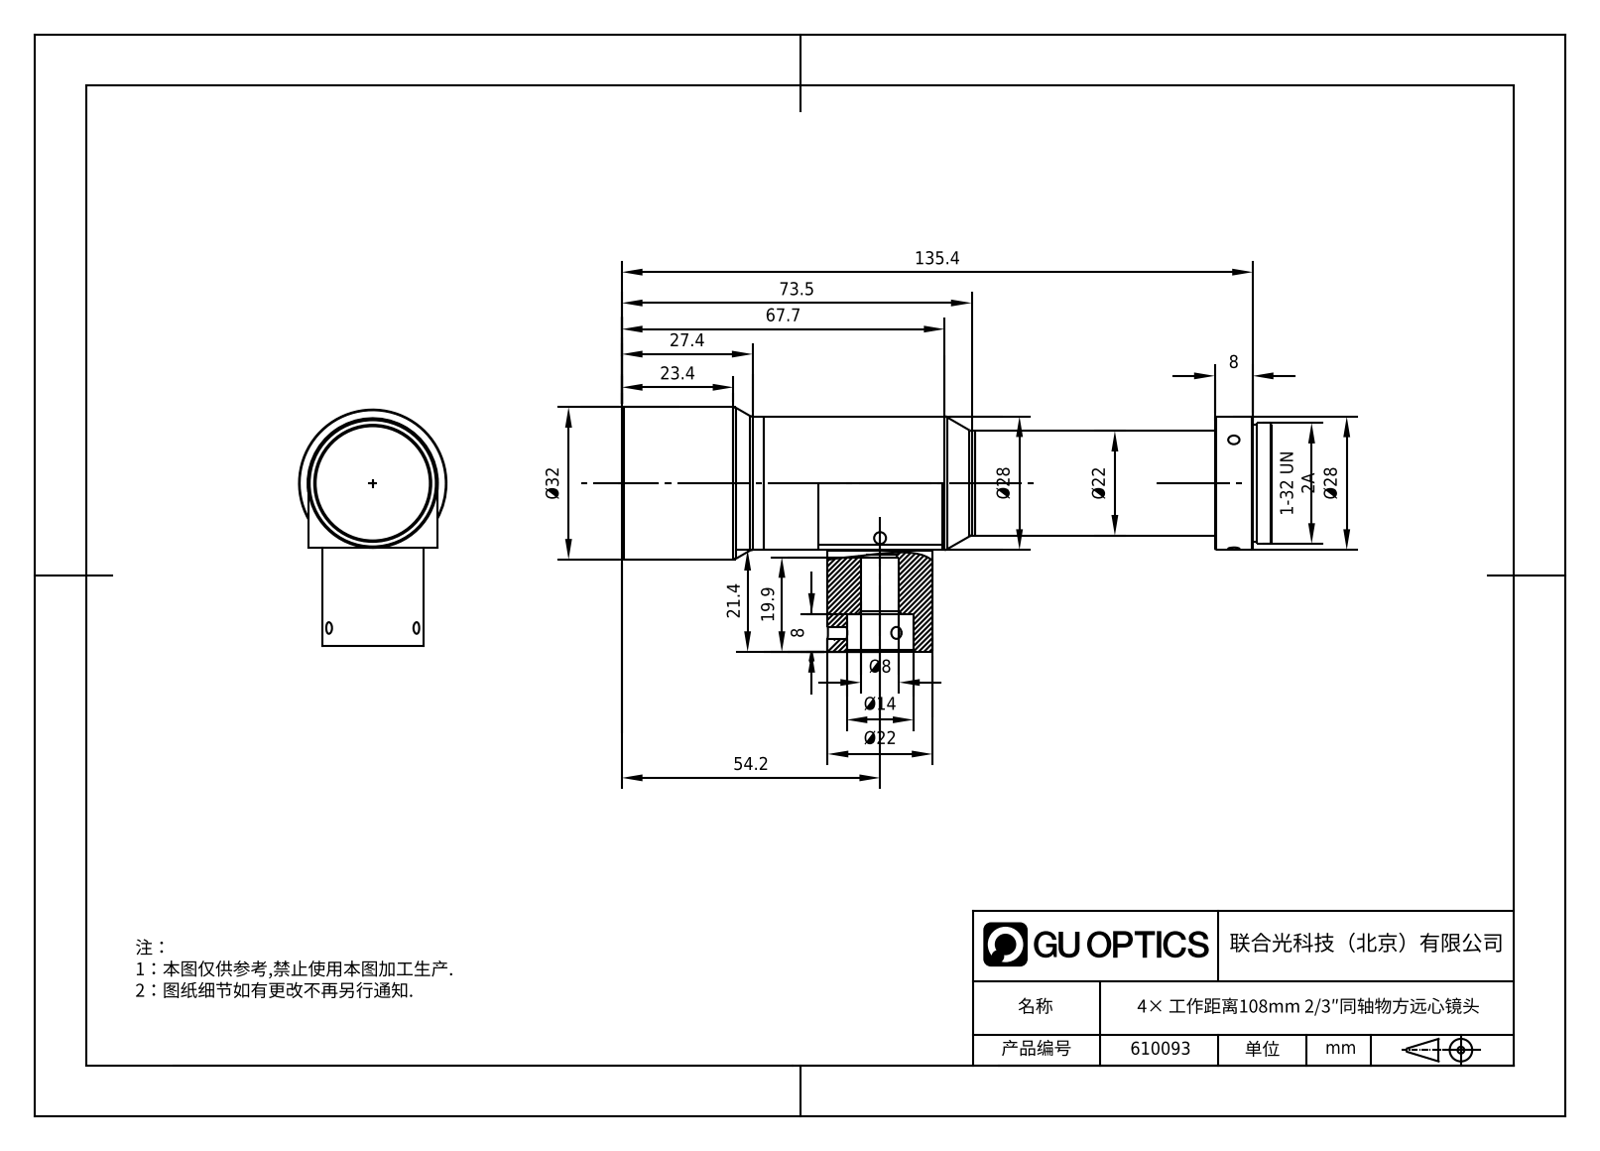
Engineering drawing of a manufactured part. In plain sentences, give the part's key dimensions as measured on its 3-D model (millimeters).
The part is named "WWH40-108CTV3". Its 3-D file was written by "SolidWorks 2017 (CONFIG_CONTROL_DESIGN)". It is 1 solid with 60 faces: 15 planar, 25 cylindrical and 20 other. Overall it measures 139.4 by 51.4 by 32 millimeters. Its volume is 85 128 cubic millimeters and its surface area 15 936 square millimeters. Round holes: 3 of diameter 3, 1 of diameter 8, 1 of diameter 14. Round bosses or shafts: 2 of diameter 22, 1 of diameter 32, 1 of diameter 28, 1 of diameter 25.4, 1 of diameter 24.4. The main face-to-face distances are 139.4, 28, 21.4, 8, 127.4, 12, 135.4, 4, 13.4, 67.2.
